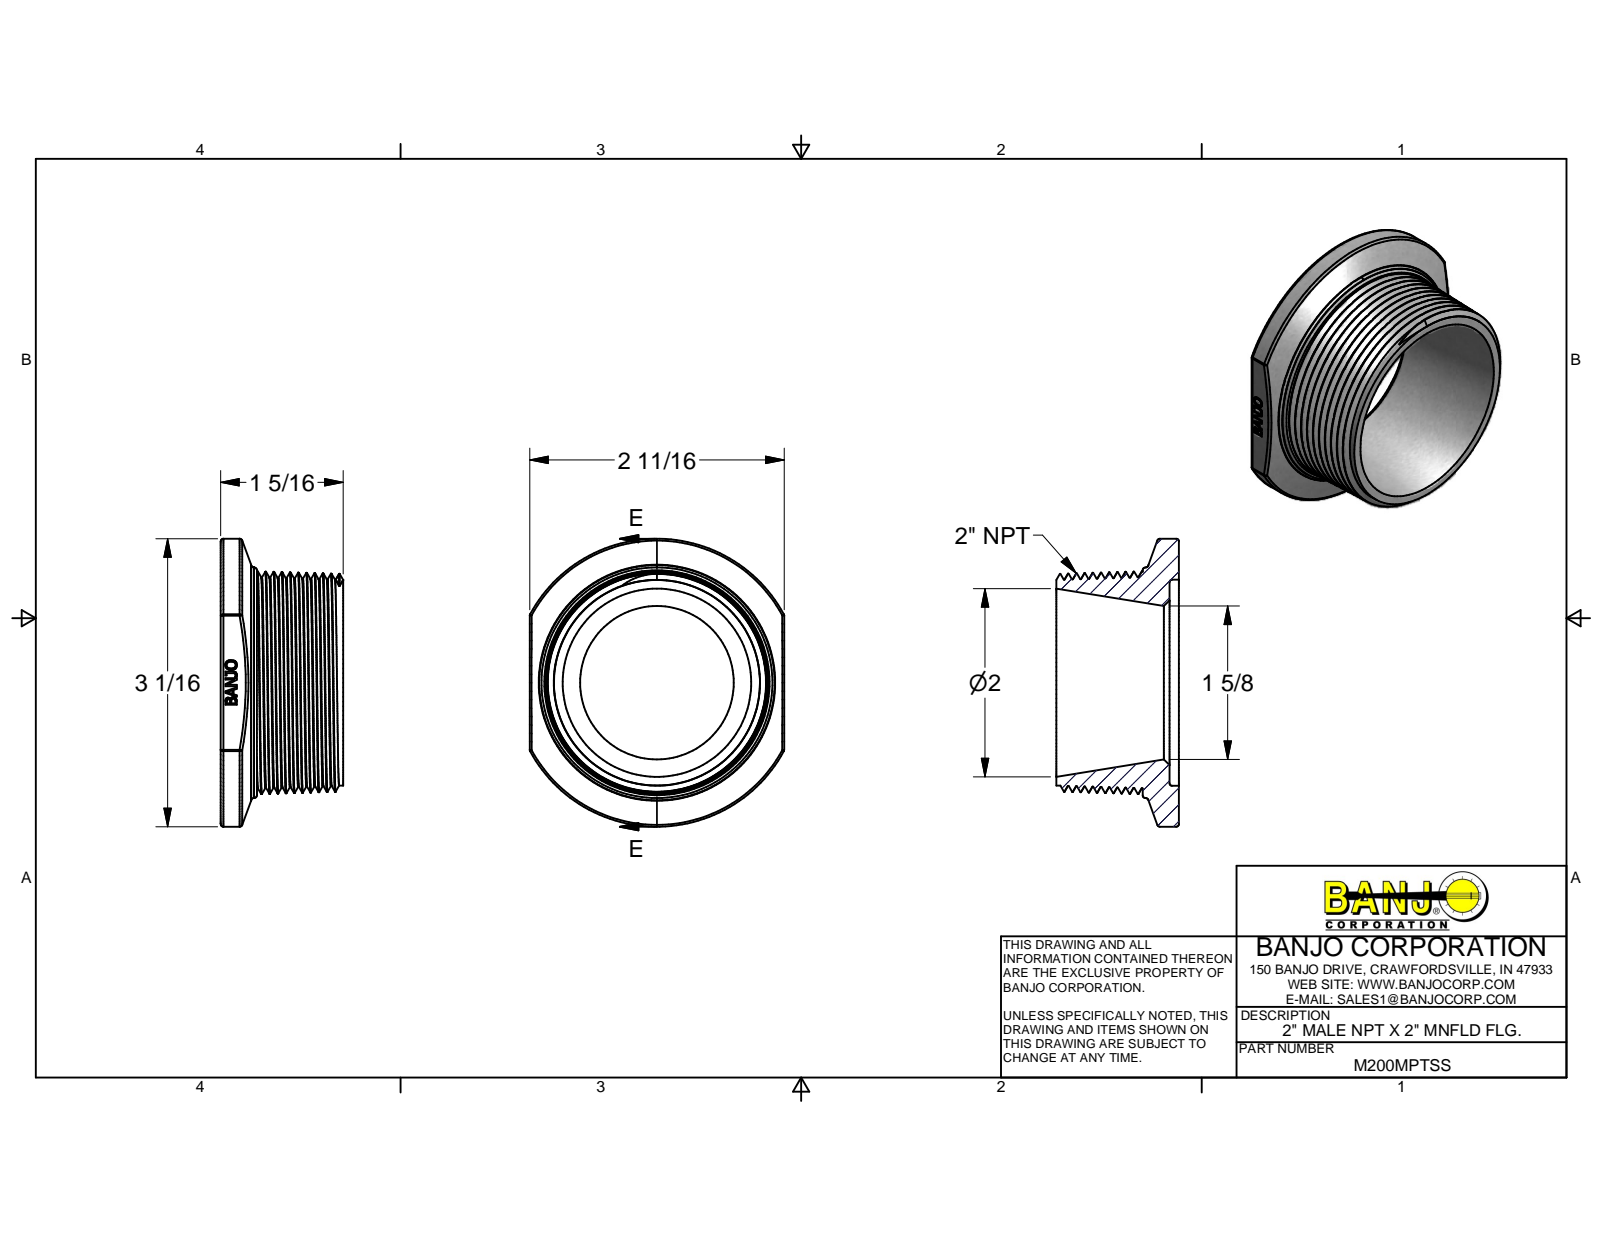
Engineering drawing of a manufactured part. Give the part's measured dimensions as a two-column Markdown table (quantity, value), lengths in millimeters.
| quantity | value |
| --- | --- |
| part name | M200MPTSS |
| STEP written by | Autodesk Inventor 2014 (AUTOMOTIVE_DESIGN) |
| units | millimeters |
| bodies | 1 solid, 267 faces (121 planar, 11 cylindrical, 135 other) |
| overall size | 77.72 × 68.58 × 33.02 |
| volume | 44 157 mm³ |
| surface area | 19 484 mm² |
| round holes (diameter × count) | 55.63 × 1 |
| round bosses / shafts (diameter × count) | 62.23 × 1 |
| partial cylindrical surfaces (radius × count) | 0.76 × 6, 15.5 × 1, 38.86 × 1 |
| main face-to-face distances | 2.54, 30.48, 33.02, 7.22, 23.26, 9.76, 68.58, 0.76, 67.82, 67.06 |
